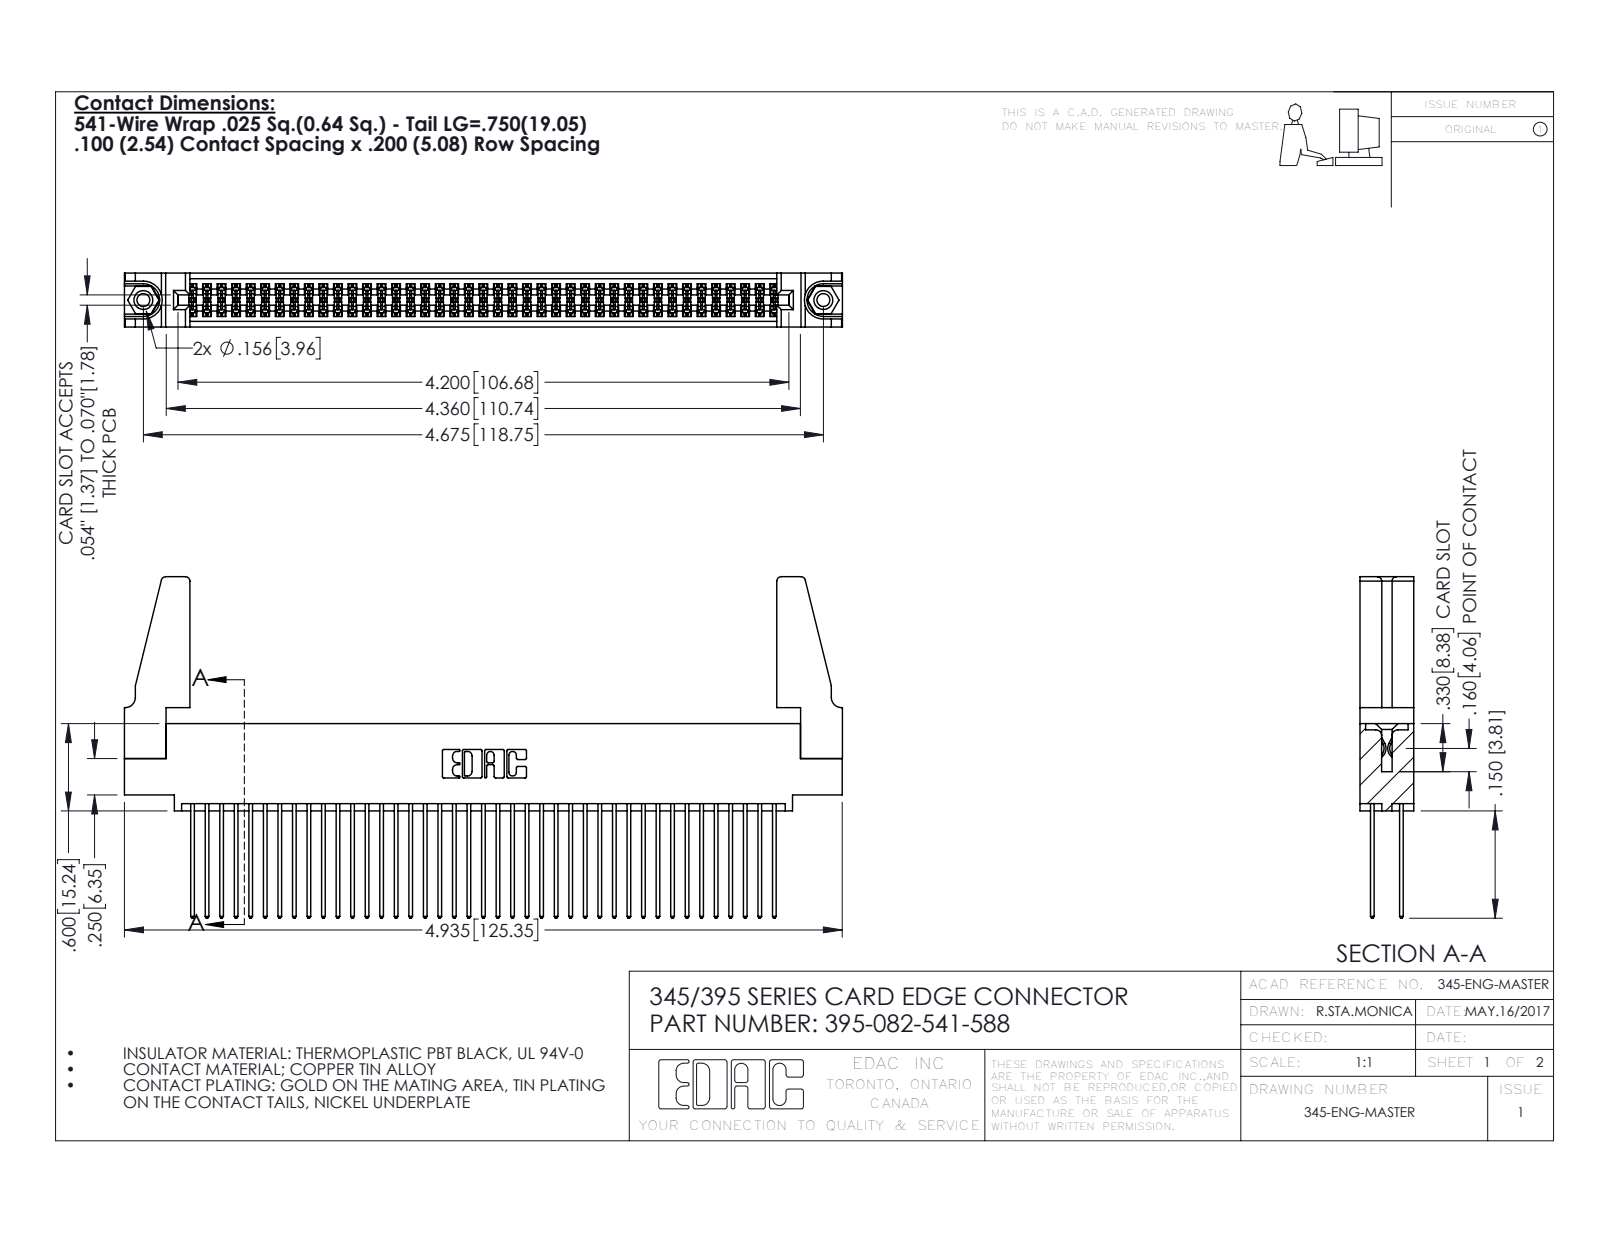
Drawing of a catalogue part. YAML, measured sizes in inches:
part_name: "395-082-541-588; 345-250-001_345-250-001-102; 345-292-001_345-293-141; 345-220-078_345-220-088 (+1 more)"
step_written_by: "SolidWorks 2016 (CONFIG_CONTROL_DESIGN)"
units: inches
bodies: {solids: 87, faces: 4354, planar: 2862, cylindrical: 1476, other: 16}
overall_size: [4.936, 2.347, 0.37]
volume: 0.965
surface_area: 37.17
round_holes:
  - {diameter: 0.089, count: 2}
  - {diameter: 0.125, count: 2}
  - {diameter: 0.156, count: 2}
  - {diameter: 0.064, count: 1}
round_bosses_or_shafts:
  - {diameter: 0.155, count: 2}
partial_cylinders:
  - {radius: 0.006, count: 123}
  - {radius: 0.01, count: 82}
  - {radius: 0.01, count: 22}
  - {radius: 0.03, count: 8}
  - {radius: 0.007, count: 6}
  - {radius: 0.031, count: 6}
  - {radius: 0.026, count: 3}
  - {radius: 0.014, count: 2}
face_to_face_distances: [0.072, 0.298, 0.2, 0.098, 0.272, 0.025, 0.37, 0.225, 0.175, 0.149]
hole_center_spacings: [0.27, 4.439, 4.675]
